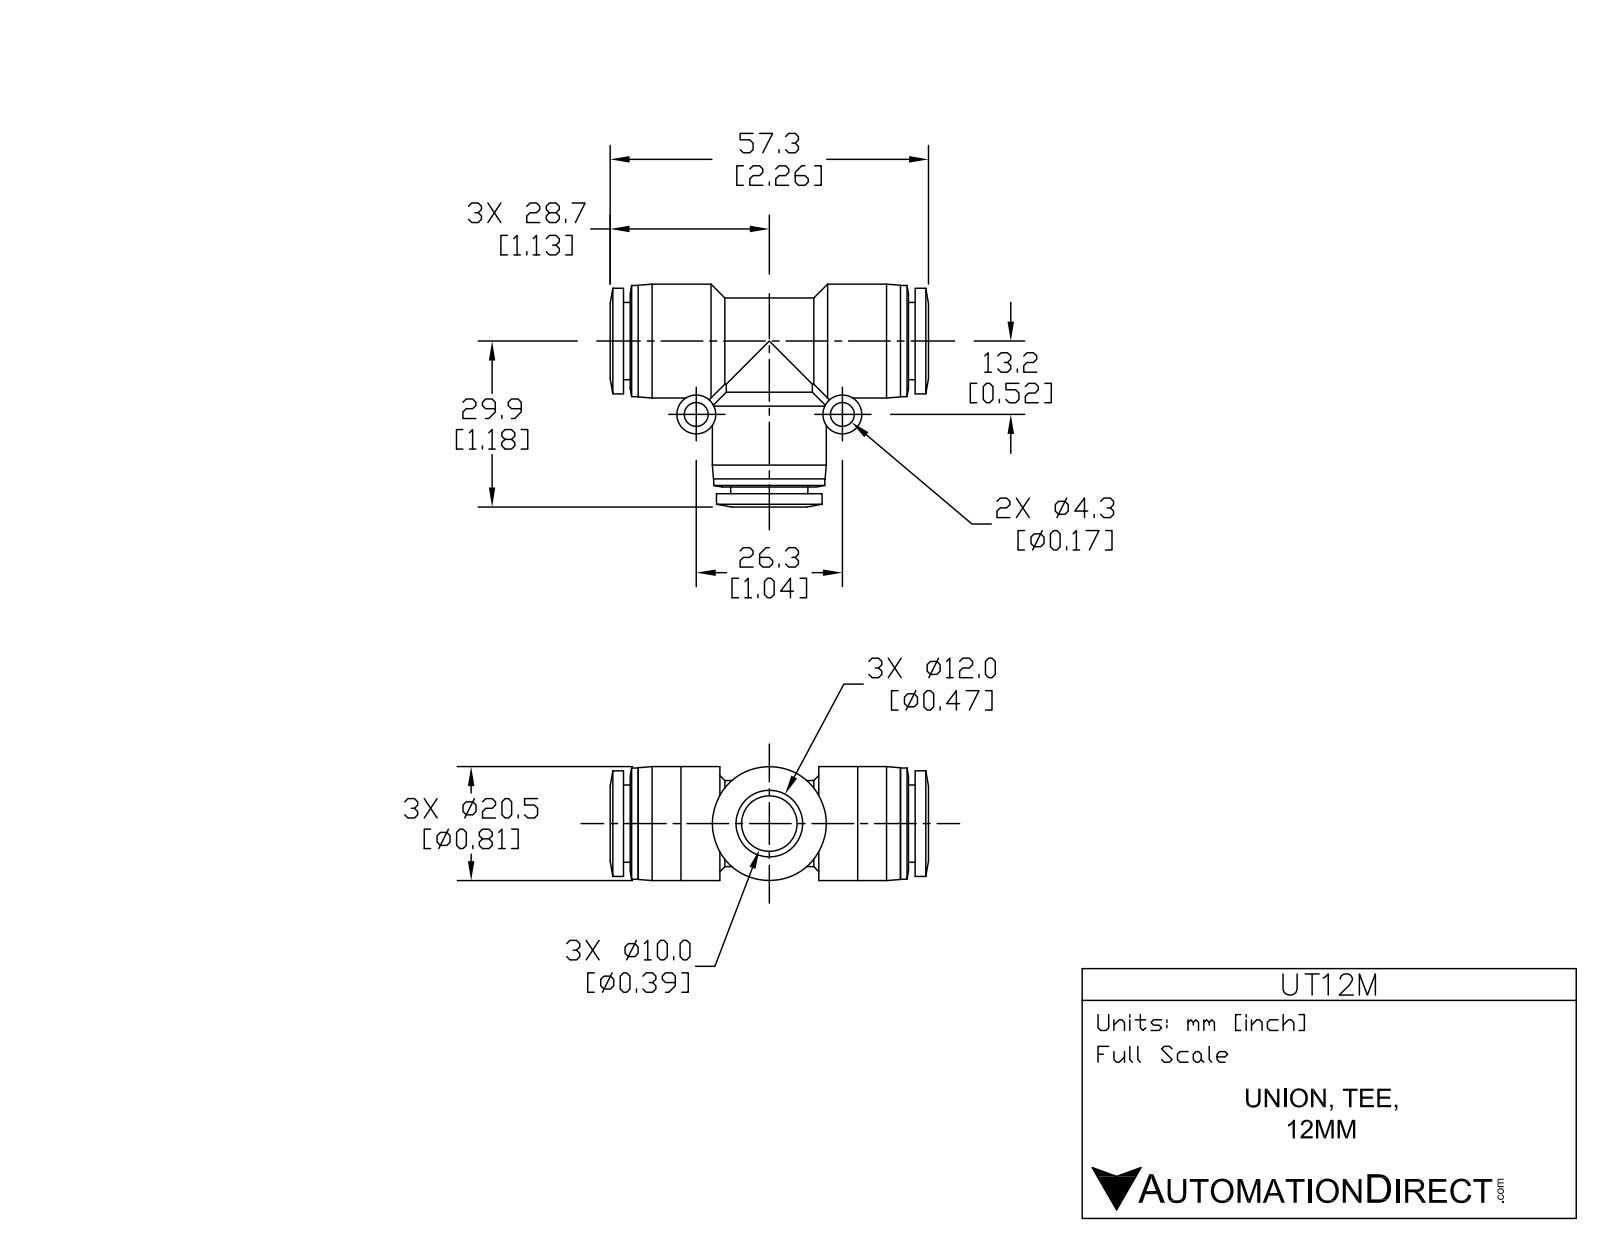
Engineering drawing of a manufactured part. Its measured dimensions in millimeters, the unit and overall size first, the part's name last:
Units: millimetres
Overall size (bounding box): 57.3 × 40.1 × 20.5
Round holes (diameter × count): ⌀4.3 ×2, ⌀10 ×2, ⌀12.2 ×2
Round bosses / shafts (diameter × count): ⌀20.5 ×2, ⌀20 ×2, ⌀19 ×2, ⌀15.5 ×2, ⌀13.9 ×2, ⌀7 ×2
Main face-to-face distances: 1.2, 20.5, 51.3, 52.5, 19.3, 32, 30.8, 50.1, 2.4, 3.6
Hole centre spacings: 24.8
Volume: 13 800 mm³ · Surface area: 10 330 mm²
Bodies: 1 solid, 97 faces (19 planar, 48 cylindrical, 30 other)
Part name (STEP PRODUCT): UT12M
STEP written by: SolidWorks 2015 (AUTOMOTIVE_DESIGN)
